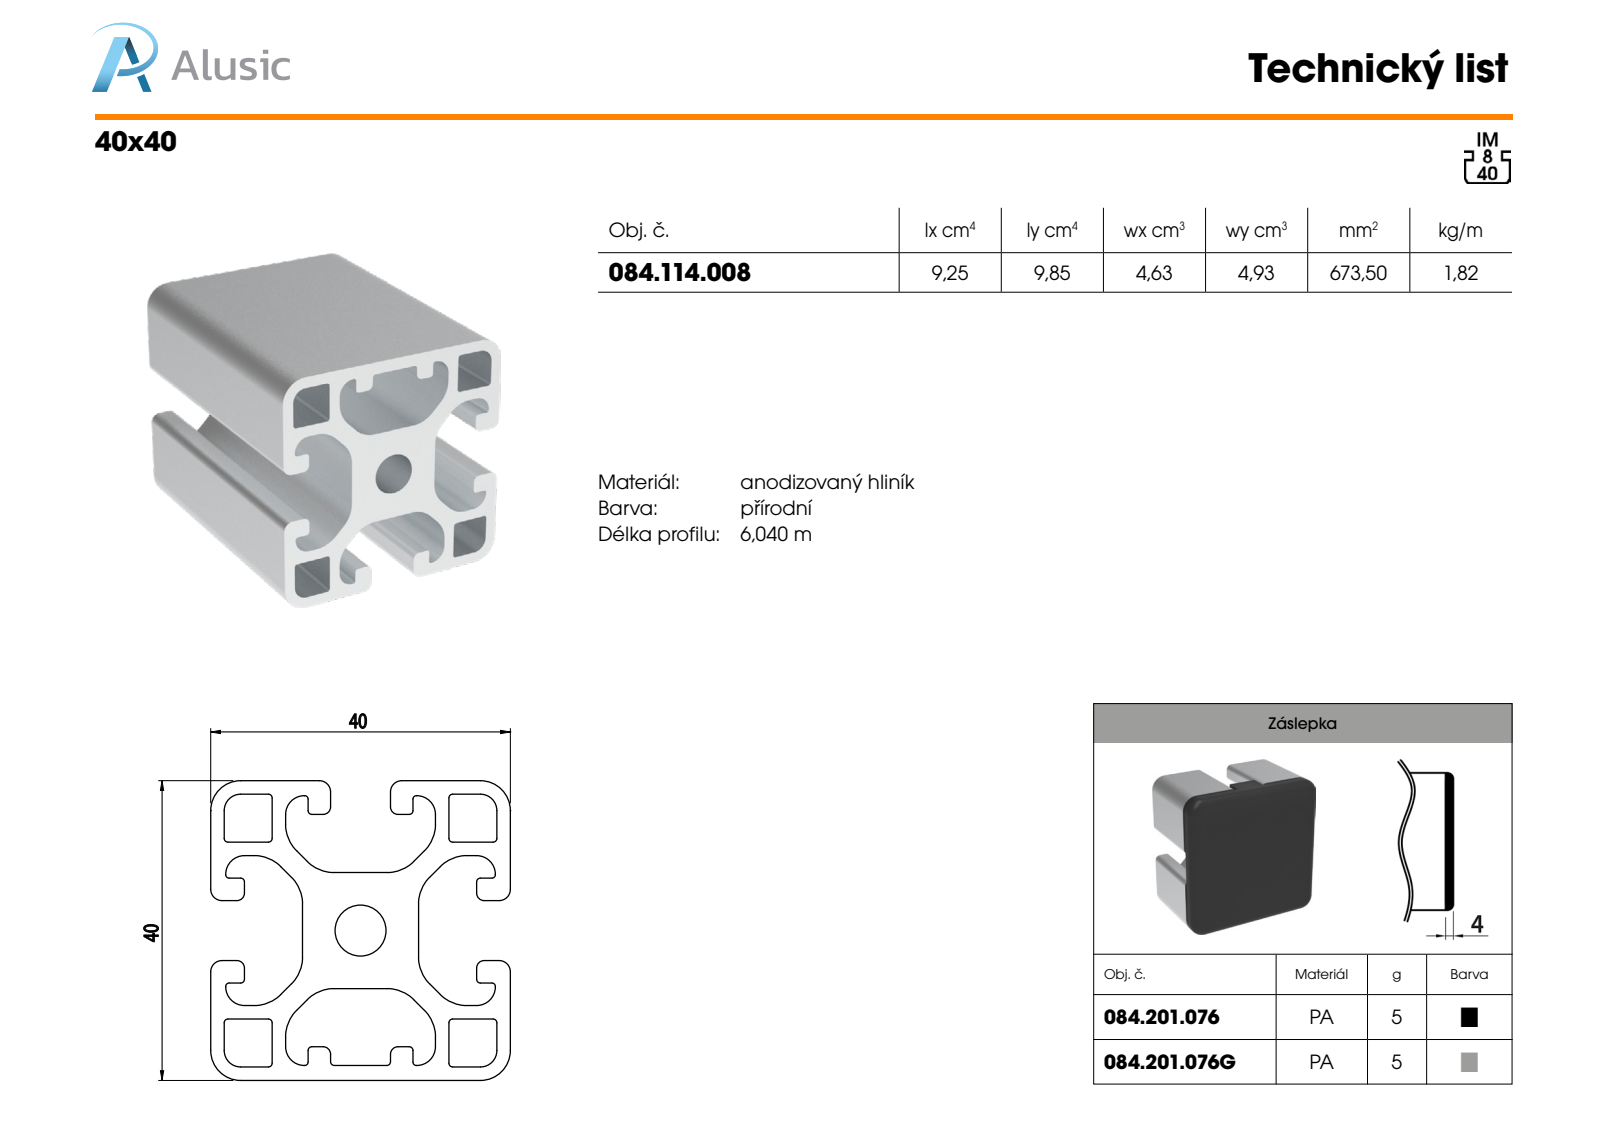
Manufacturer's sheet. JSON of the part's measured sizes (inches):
{"part_name": "084.114.008", "step_written_by": "SolidWorks 2018 (AUTOMOTIVE_DESIGN)", "units": "inches", "bodies": {"solids": 1, "faces": 148, "planar": 70, "cylindrical": 78, "other": 0}, "overall_size": [3.937, 1.575, 1.575], "volume_in3": 4.11, "surface_area_in2": 75.32, "round_holes": [[0.268, 1]], "partial_cylinders_radius": [[0.02, 22], [0.197, 16], [0.018, 8], [0.039, 8], [0.098, 8], [0.059, 6], [0.087, 4], [0.157, 4]], "face_to_face_distances": [0.323, 1.252, 1.575, 0.77, 0.071, 1.181, 1.504, 0.252, 0.482, 1.093]}
